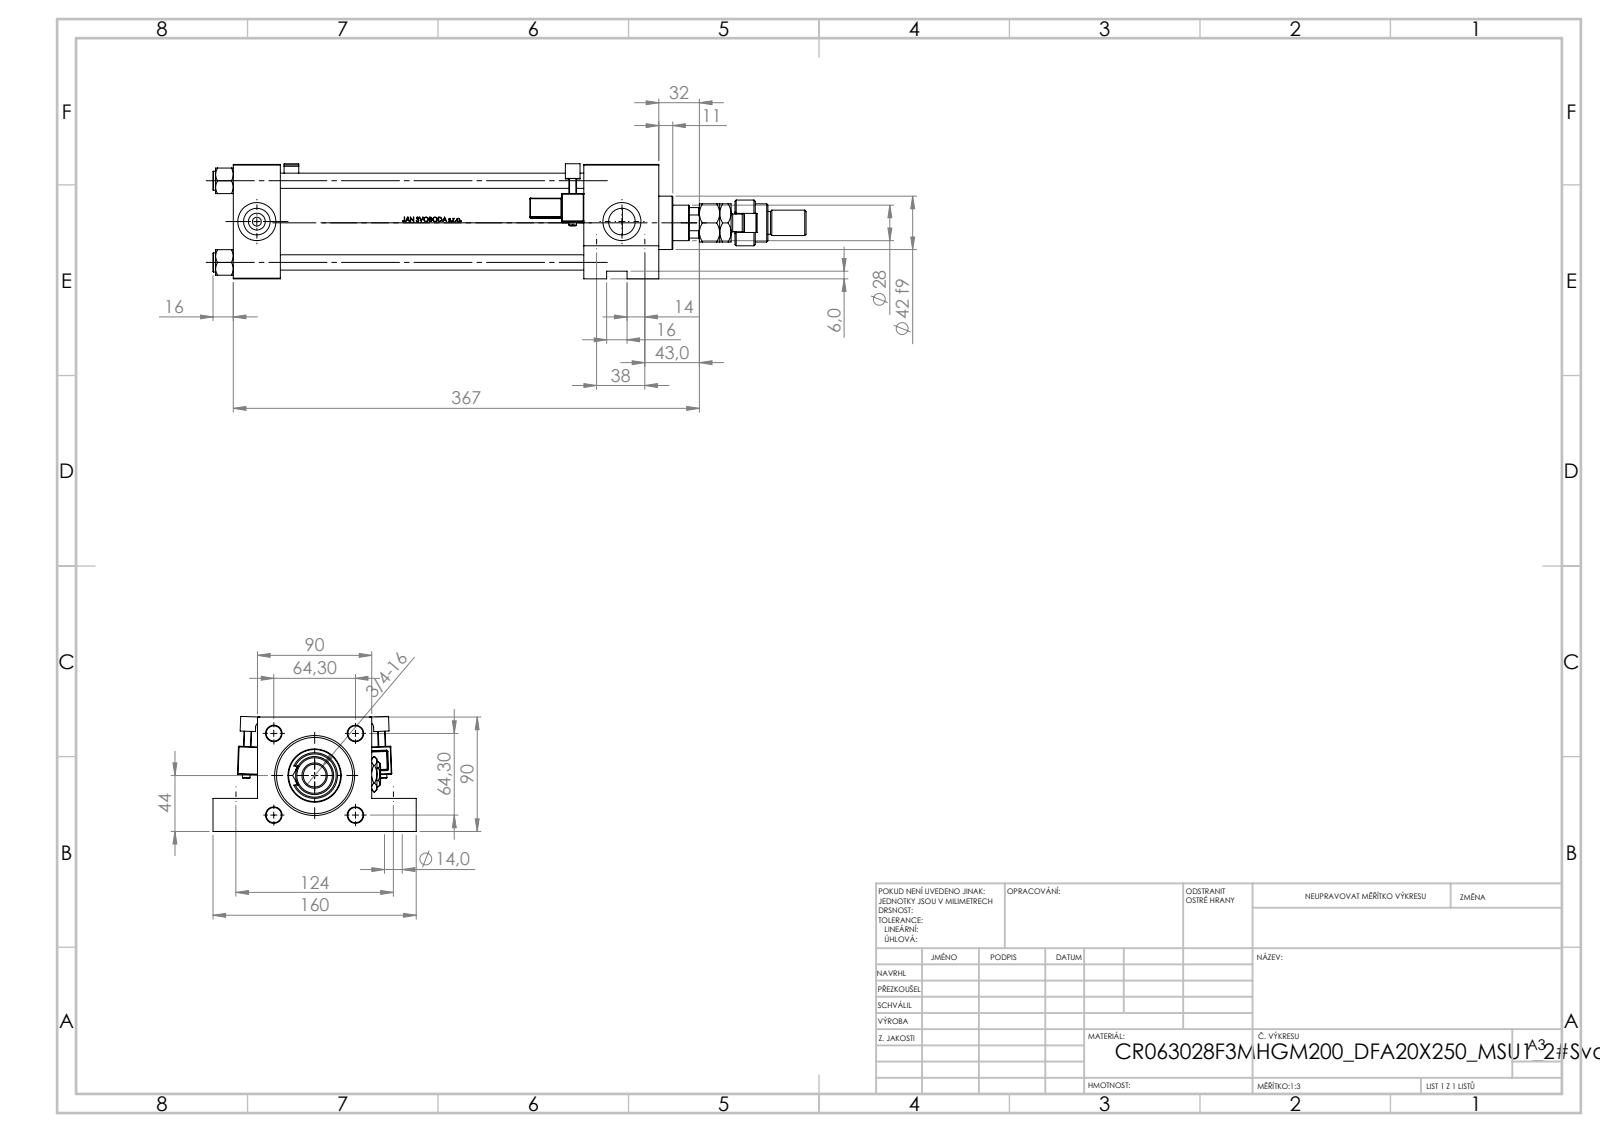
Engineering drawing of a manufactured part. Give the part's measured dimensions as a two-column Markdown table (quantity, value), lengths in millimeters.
| quantity | value |
| --- | --- |
| part name | V215CR_F_Body; V215CR_MSU; V215CR_VCP_F; Zatka_pro_OIL_PORT (+5 more) |
| STEP written by | SolidWorks 2019 (CONFIG_CONTROL_DESIGN) |
| units | millimeters |
| bodies | 17 solids, 1439 faces (570 planar, 207 cylindrical, 662 other) |
| overall size | 467 × 160 × 90.53 |
| volume | 1 417 000 mm³ |
| surface area | 341 790 mm² |
| round holes (diameter × count) | 12 × 4, 14 × 4, 20.96 × 3, 30 × 3, 7 × 2, 18.5 × 1, 20 × 1, 28 × 1, 31 × 1, 50 × 1, 60 × 1, 63 × 1 |
| round bosses / shafts (diameter × count) | 15 × 4, 6 × 2, 69 × 1, 42 × 1, 36 × 1, 30 × 1, 22 × 1, 20 × 1 |
| partial cylindrical surfaces (radius × count) | 0.5 × 48, 1 × 2, 2.5 × 2, 4 × 2, 7.5 × 1, 12 × 1, 13.5 × 1 |
| main face-to-face distances | 90, 37, 335, 298, 59, 276, 239, 26, 64, 35 |
| hole center spacings | 64.3, 38, 44.77, 46.18, 90.93, 124, 129.69, 10 |
